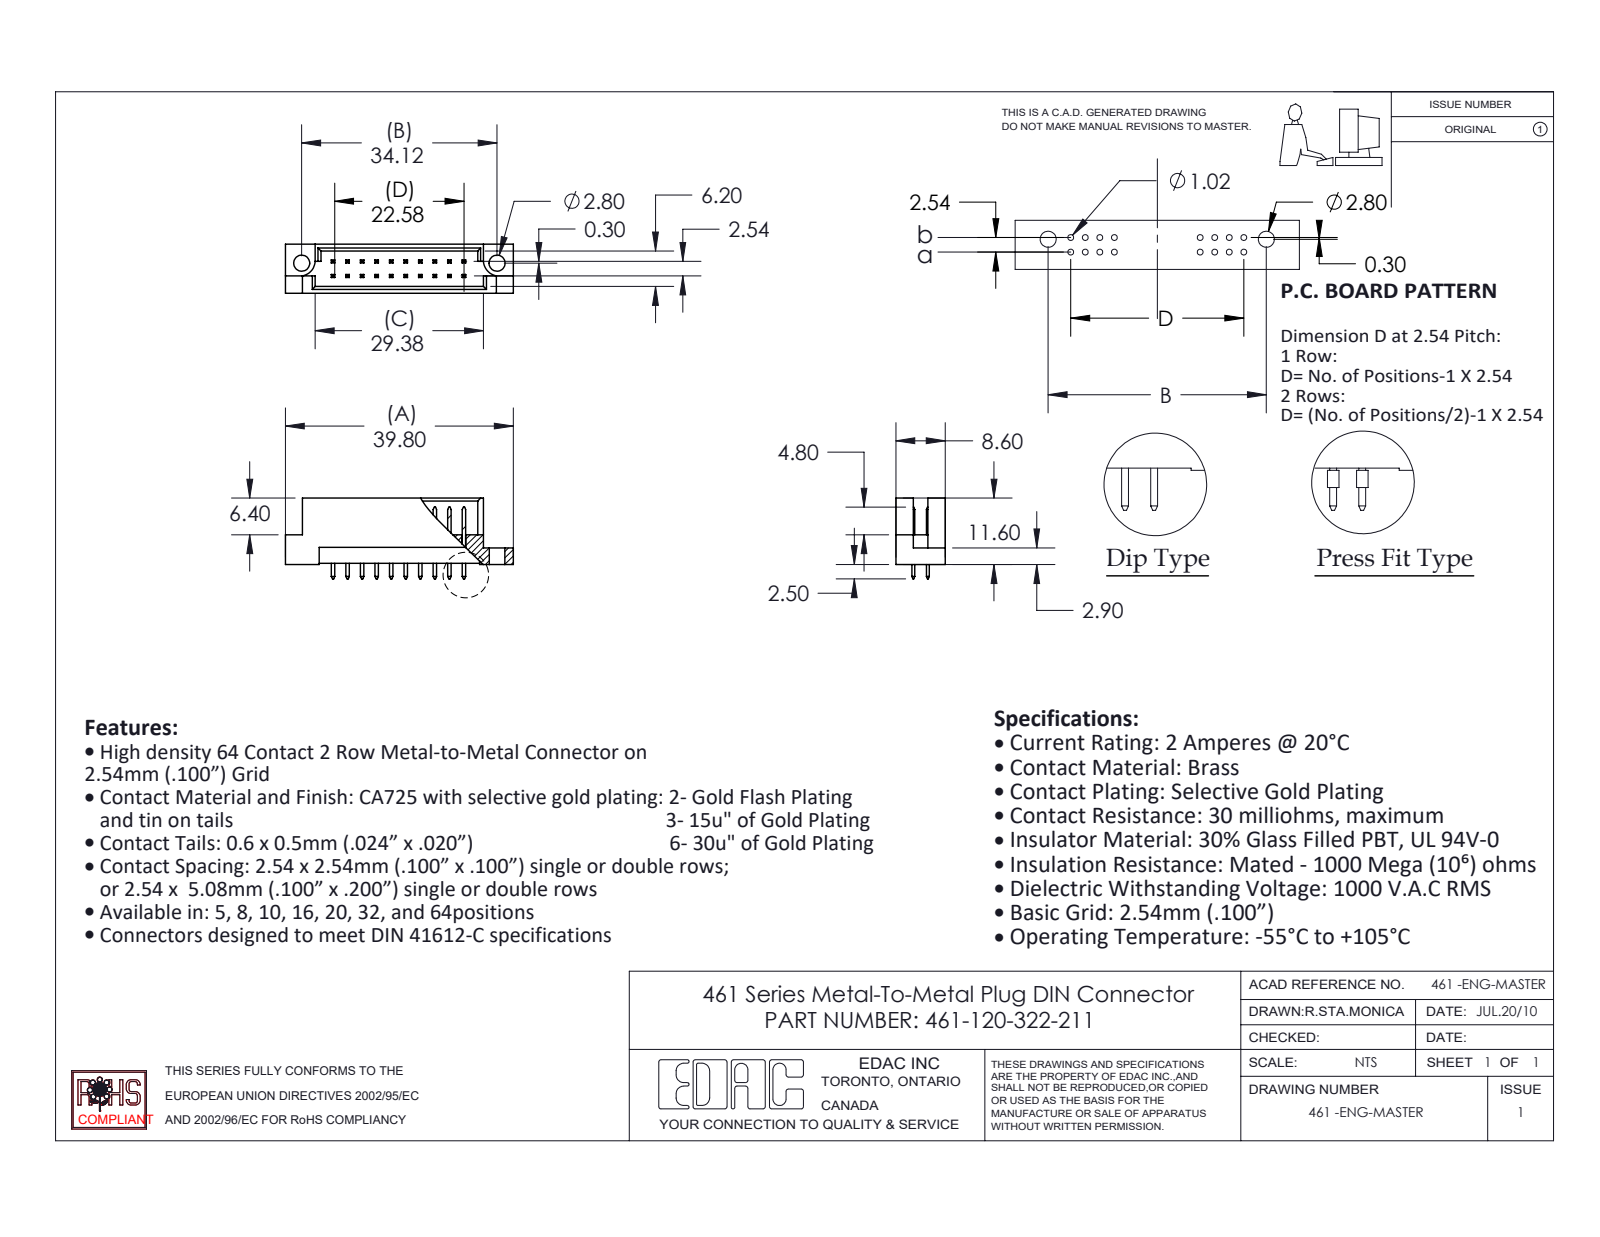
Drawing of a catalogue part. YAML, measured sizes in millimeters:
part_name: "461 Part_20; 461-290_22; 461-120-322-211"
step_written_by: "SolidWorks 2020 (CONFIG_CONTROL_DESIGN)"
units: millimeters
bodies: {solids: 21, faces: 408, planar: 402, cylindrical: 6, other: 0}
overall_size: [39.8, 14.1, 8.6]
volume: 1977
surface_area: 2880
round_holes:
  - {diameter: 2.8, count: 2}
partial_cylinders:
  - {radius: 2.8, count: 2}
face_to_face_distances: [1.2, 7.4, 2.54, 8.6, 6.2, 3.28, 5.32, 2.08, 4.12, 2.78]
hole_center_spacings: [34.12]
